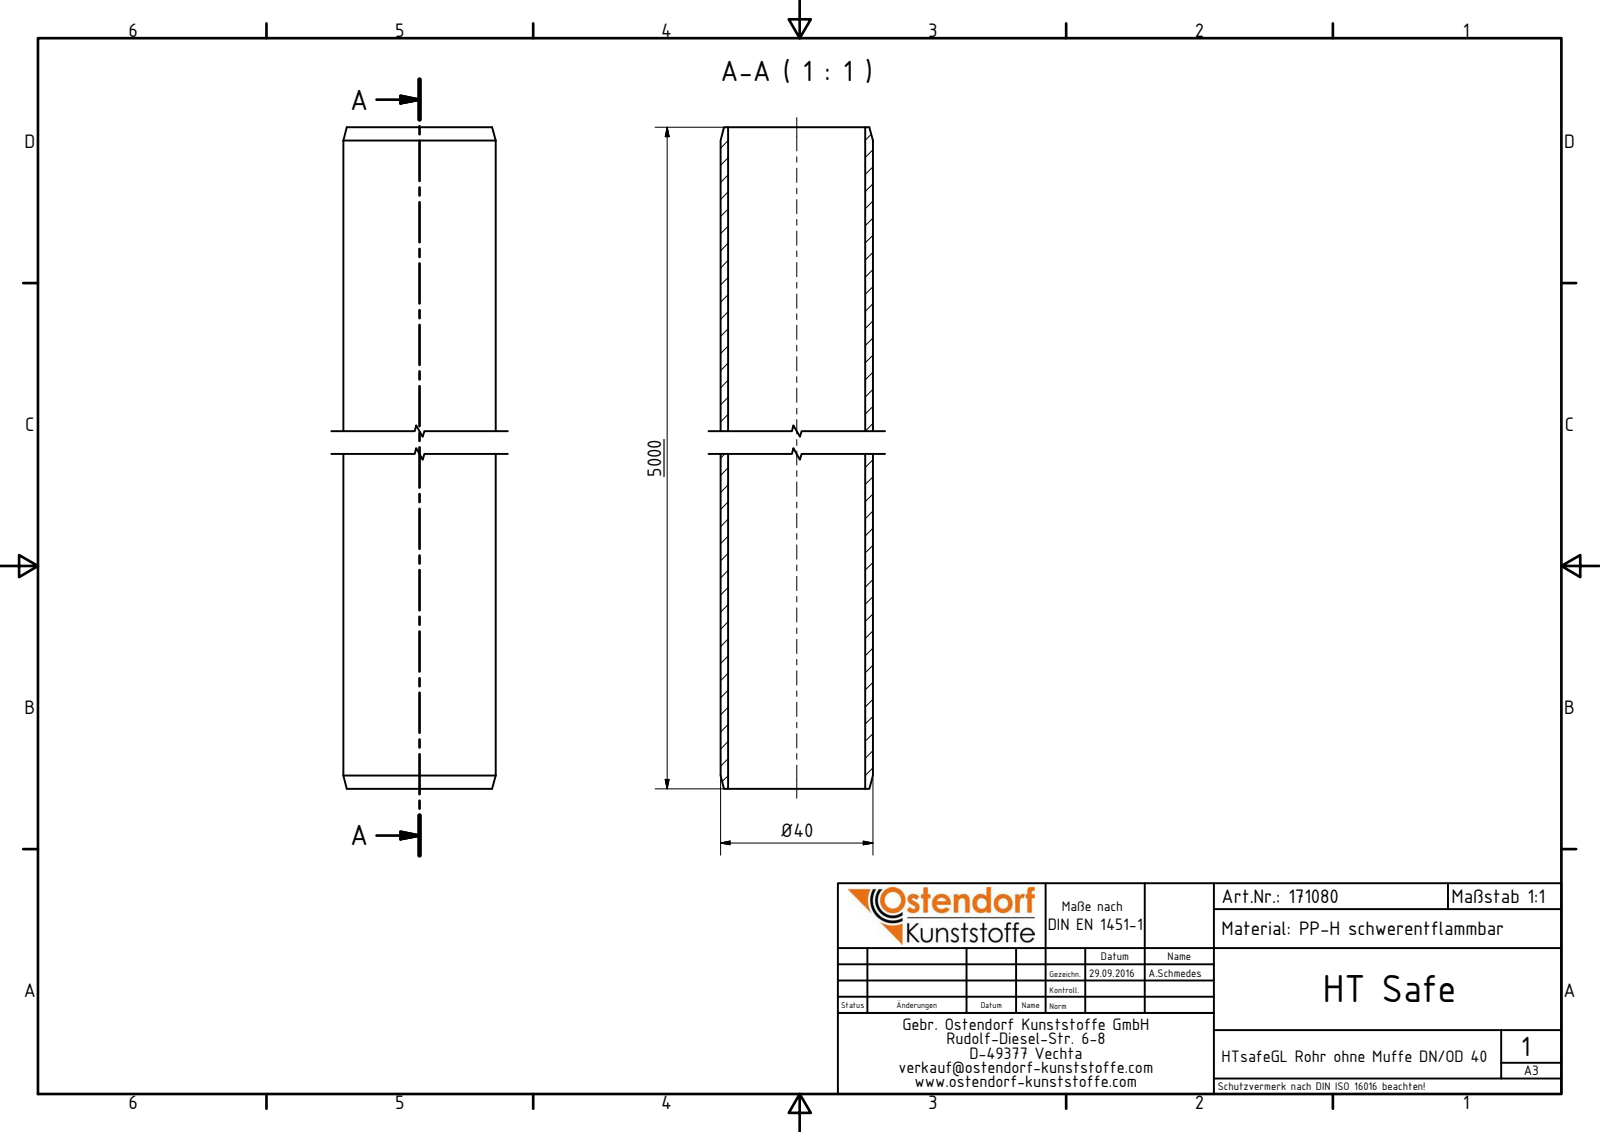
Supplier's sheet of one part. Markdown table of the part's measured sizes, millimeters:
| quantity | value |
| --- | --- |
| part name | 171080 HTsafeGL DN_OD 40x5000 |
| STEP written by | Autodesk Inventor 2016 (AUTOMOTIVE_DESIGN) |
| units | millimeters |
| bodies | 1 solid, 6 faces (2 planar, 2 cylindrical, 2 other) |
| overall size | 5000 × 40 × 40 |
| volume | 1 193 000 mm³ |
| surface area | 1 194 000 mm² |
| round holes (diameter × count) | 36 × 1 |
| round bosses / shafts (diameter × count) | 40 × 1 |
| main face-to-face distances | 5000 |
